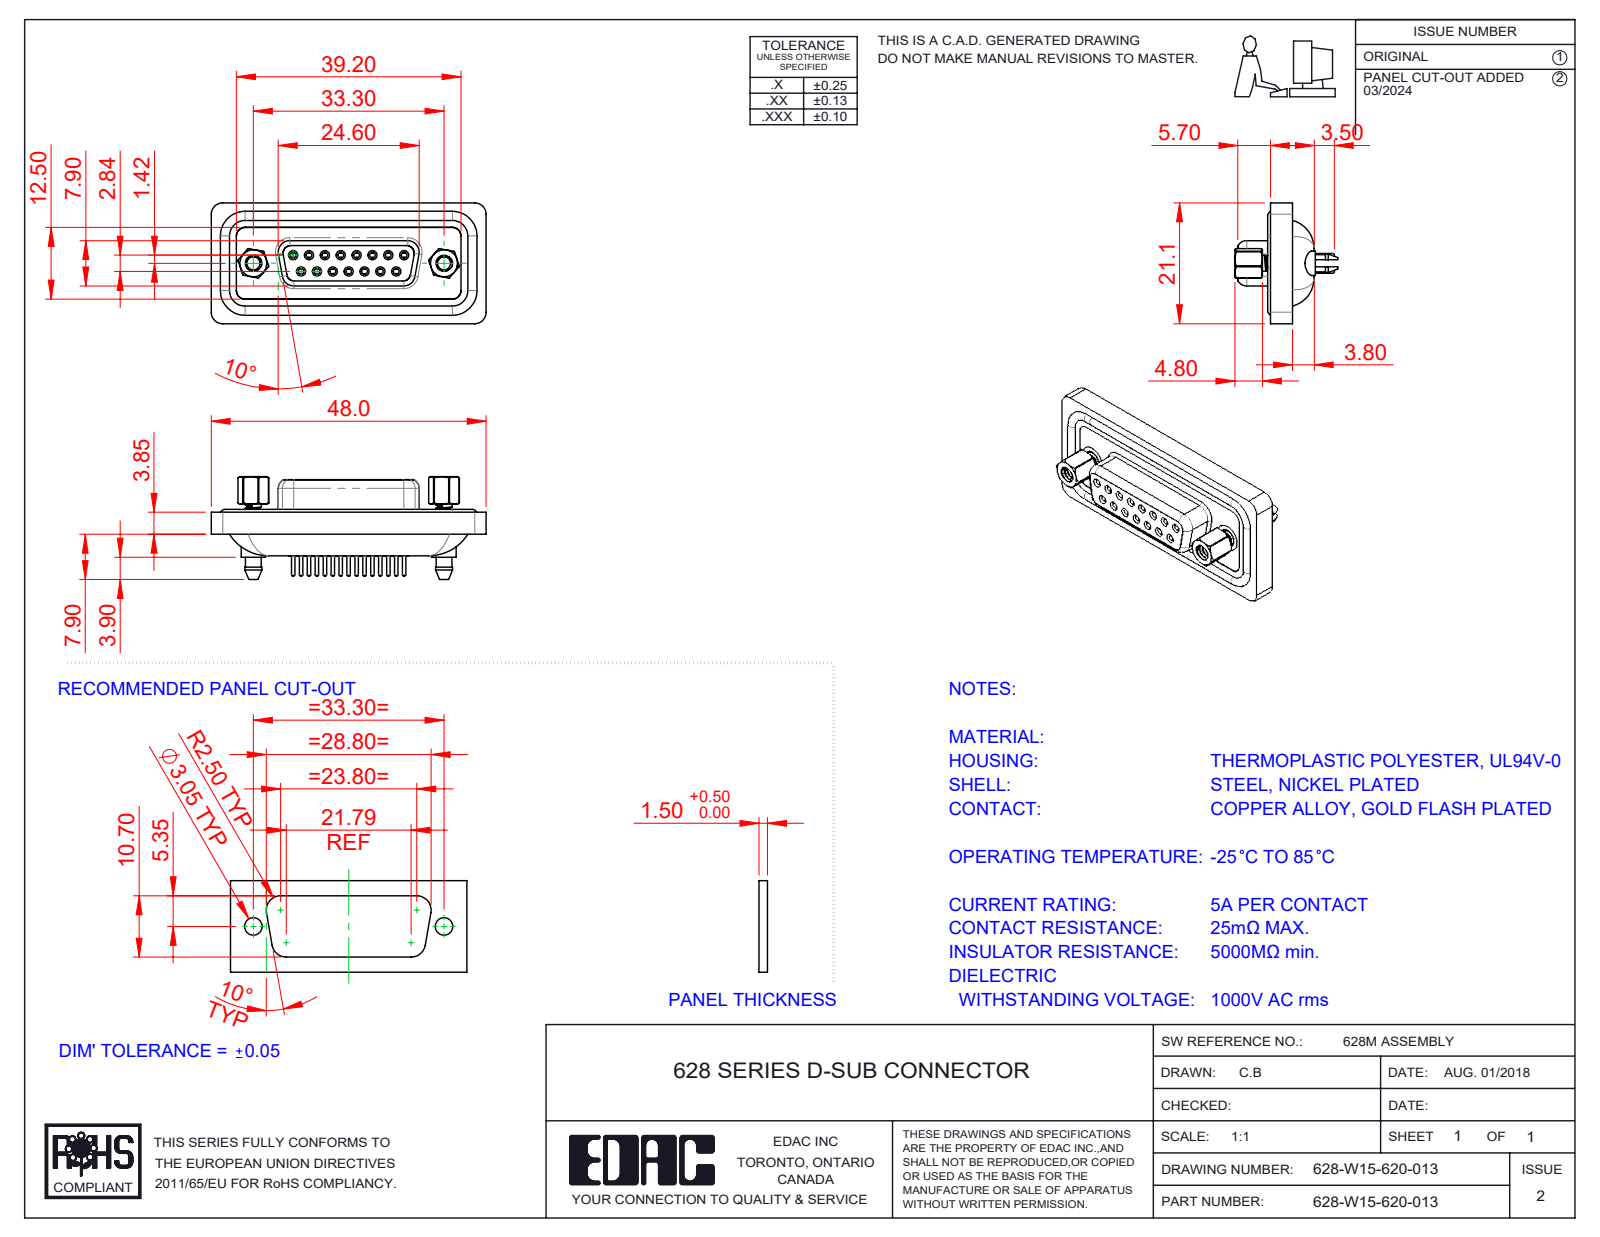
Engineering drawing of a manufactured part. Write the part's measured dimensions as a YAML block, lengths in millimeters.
part_name: "628W Contact Row 2_20; 628W 4-40 Hex Standoff; 628W Shell Front_15 Contacts; 628W Housing_15 Contacts (+4 more)"
step_written_by: "SolidWorks 2020 (CONFIG_CONTROL_DESIGN)"
units: millimeters
bodies: {solids: 23, faces: 1326, planar: 340, cylindrical: 567, other: 419}
overall_size: [48, 21.1, 17.45]
volume: 6429
surface_area: 10008
round_holes:
  - {diameter: 1, count: 15}
  - {diameter: 1.1, count: 15}
  - {diameter: 1.5, count: 15}
  - {diameter: 1.7, count: 15}
  - {diameter: 1.8, count: 15}
  - {diameter: 2, count: 15}
  - {diameter: 2.26, count: 2}
  - {diameter: 2.29, count: 2}
  - {diameter: 4, count: 2}
  - {diameter: 4.25, count: 2}
  - {diameter: 4.8, count: 2}
round_bosses_or_shafts:
  - {diameter: 1.6, count: 19}
  - {diameter: 2.2, count: 15}
  - {diameter: 0.6, count: 15}
  - {diameter: 1.5, count: 7}
  - {diameter: 5.4, count: 2}
  - {diameter: 4.9, count: 2}
  - {diameter: 2.79, count: 2}
partial_cylinders:
  - {radius: 1.5, count: 16}
  - {radius: 2, count: 16}
  - {radius: 1.35, count: 8}
  - {radius: 1.6, count: 6}
  - {radius: 0.5, count: 4}
  - {radius: 0.9, count: 4}
  - {radius: 1.75, count: 4}
  - {radius: 2.7, count: 4}
face_to_face_distances: [0.4, 1.1, 2.75, 0.5, 3.75, 8.45, 7.45, 7.5, 13.65, 4.1]
hole_center_spacings: [3.16, 2.77, 5.54, 8.31, 5.03, 5.04, 7.48, 7.49]
